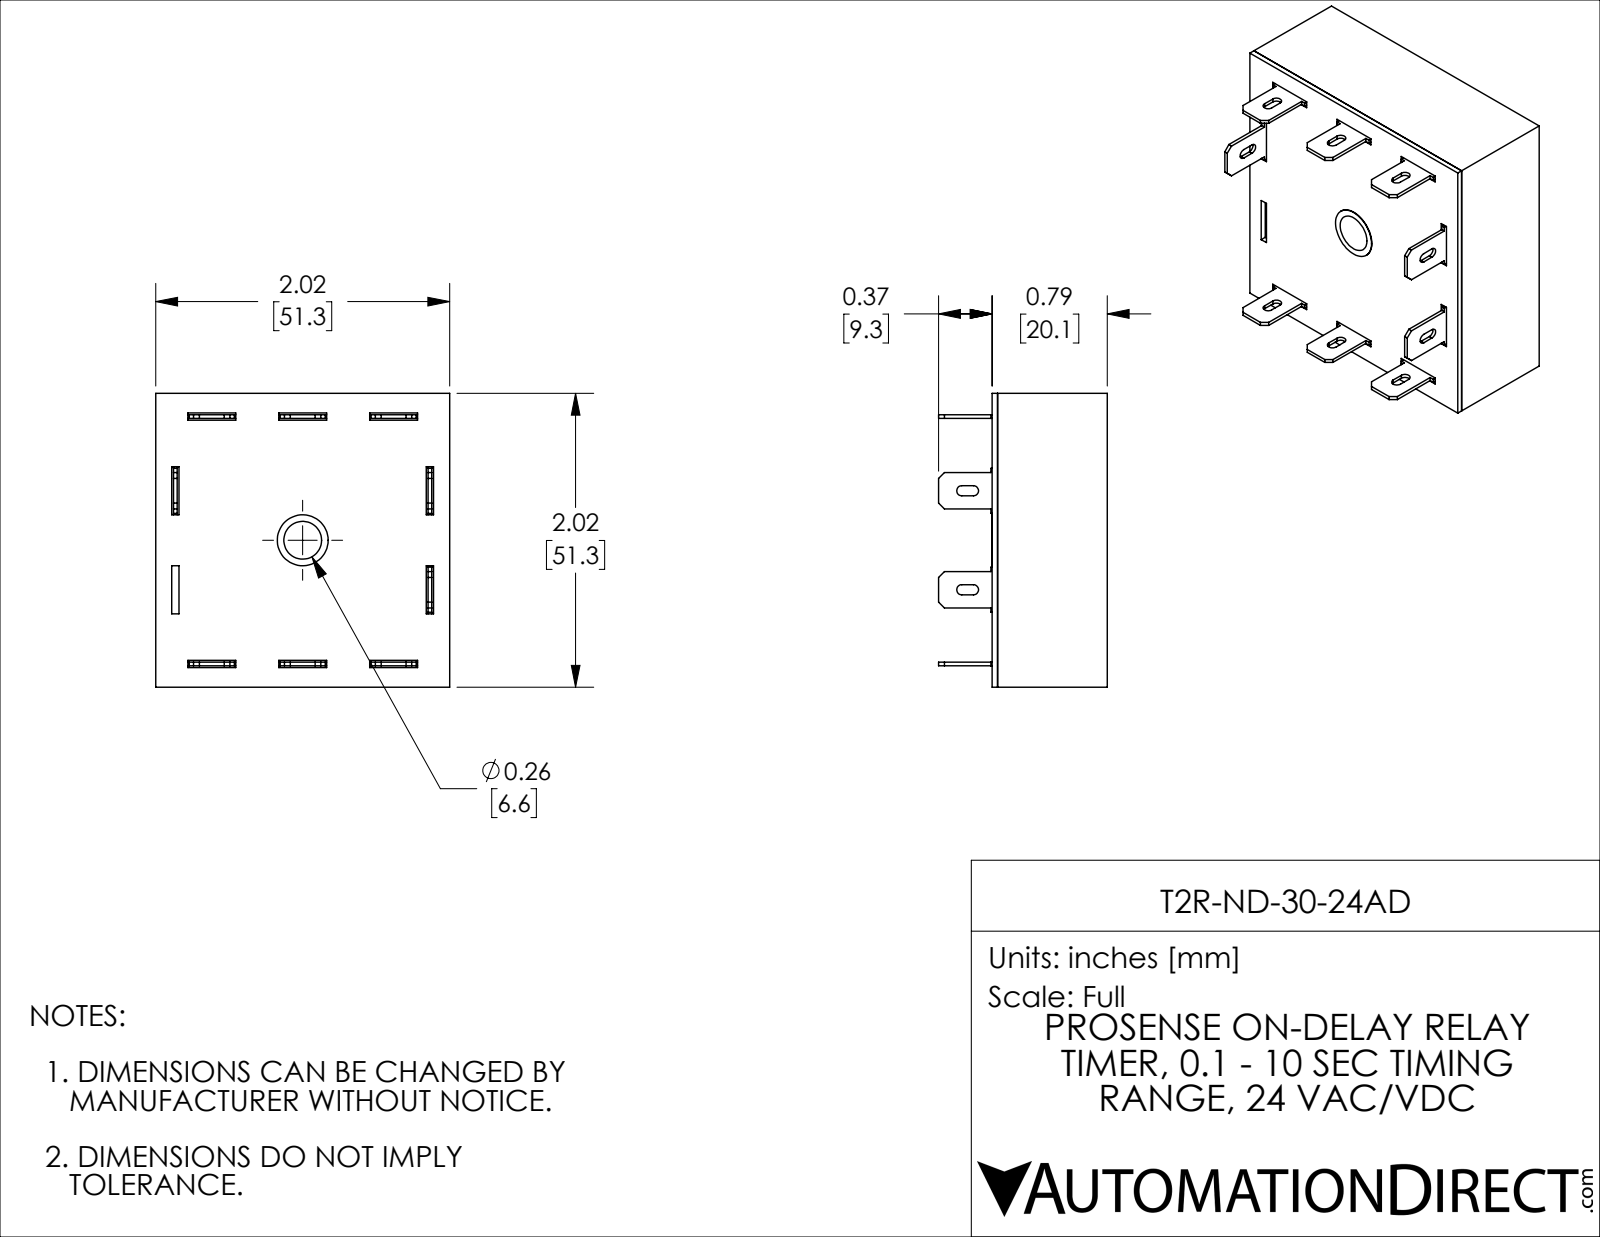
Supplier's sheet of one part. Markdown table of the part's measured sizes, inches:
| quantity | value |
| --- | --- |
| part name | T2R-ND-30-24AD |
| STEP written by | SolidWorks 2021 (CONFIG_CONTROL_DESIGN) |
| units | inches |
| bodies | 11 solids, 280 faces (256 planar, 22 cylindrical, 2 other) |
| overall size | 2.02 × 2.02 × 1.16 |
| volume | 0.682 in³ |
| surface area | 36.12 in² |
| round holes (diameter × count) | 0.35 × 1 |
| partial cylindrical surfaces (radius × count) | 0.035 × 10 |
| main face-to-face distances | 0.045, 1.975, 0.754, 0.792, 0.038, 0.709, 0.747, 2.02, 0.147, 1.872 |
